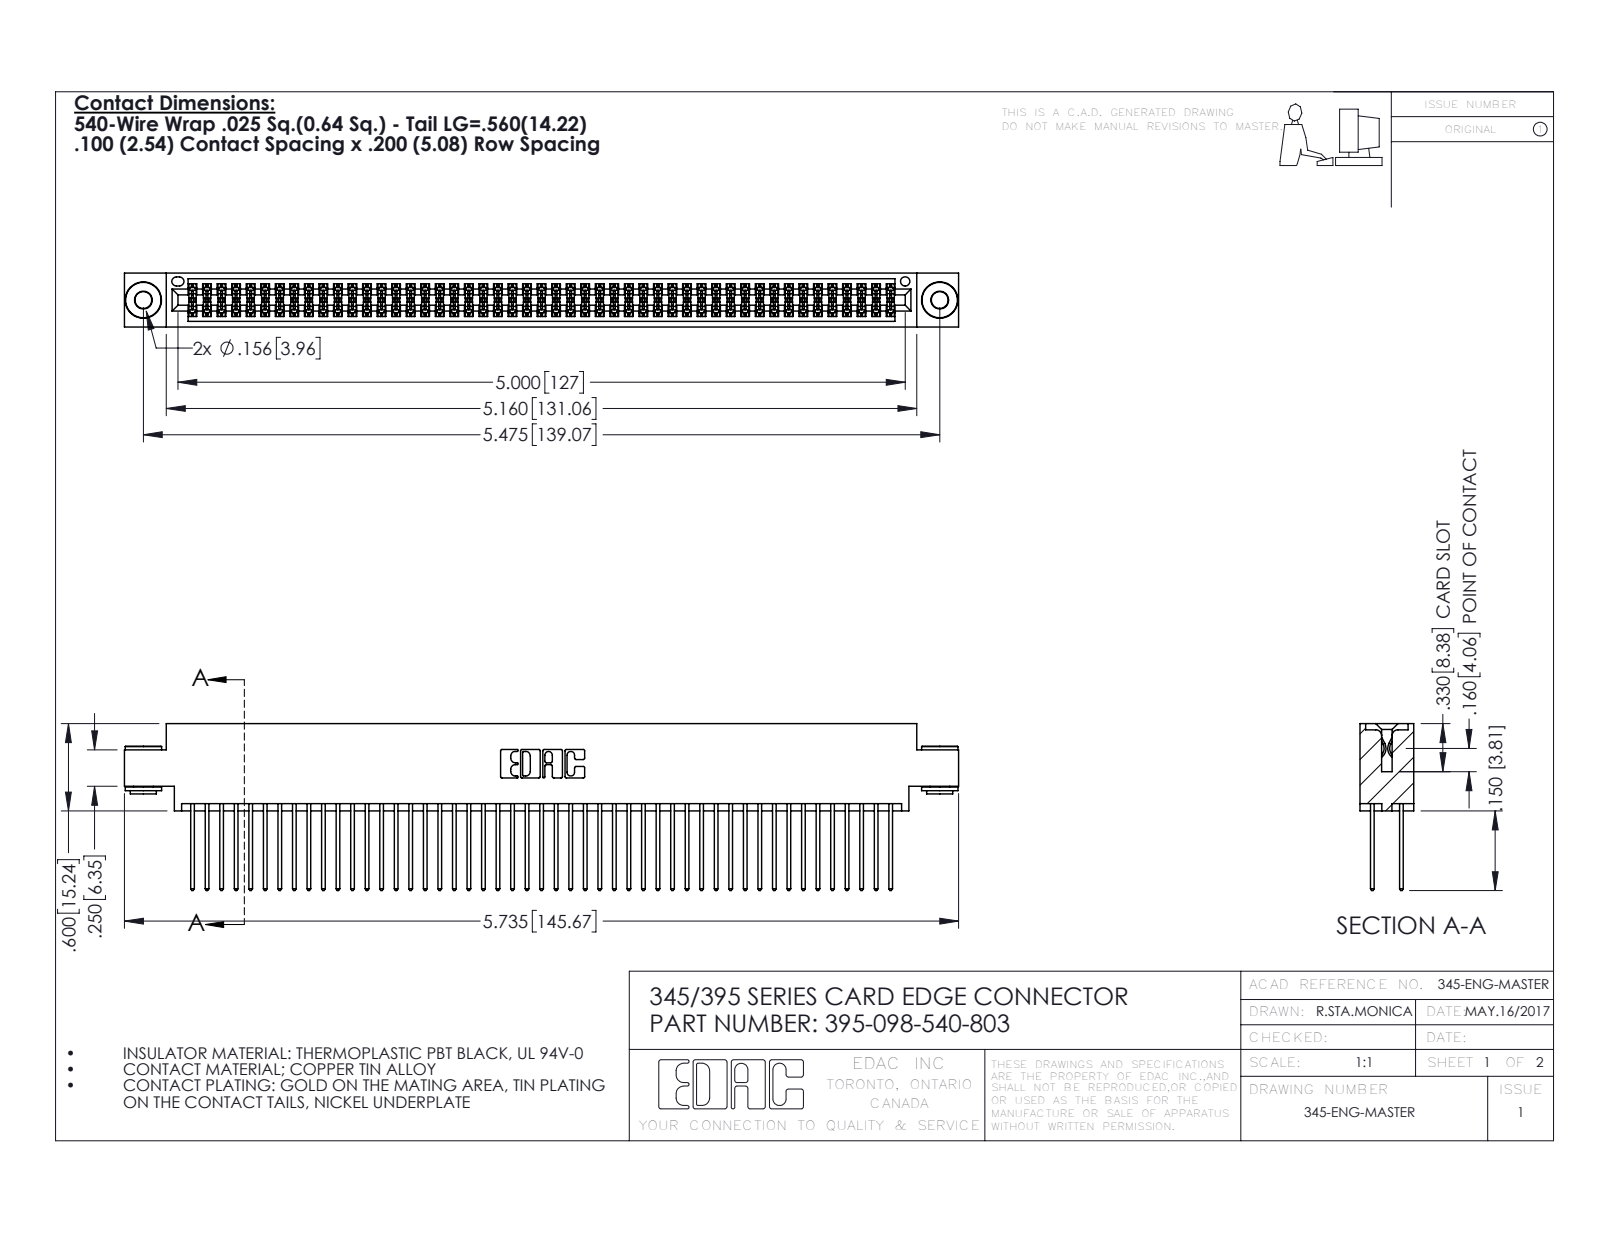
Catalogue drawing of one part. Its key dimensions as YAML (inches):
part_name: "345 Part_0.170 Offset - 0.156 Dia-TH; 345-250-002_345-250-002-102; 395-098-540-803; 345-292-001_345-293-140"
step_written_by: "SolidWorks 2016 (CONFIG_CONTROL_DESIGN)"
units: inches
bodies: {solids: 101, faces: 5068, planar: 3328, cylindrical: 1732, other: 8}
overall_size: [5.735, 1.147, 0.37]
volume: 0.884
surface_area: 36.63
round_holes:
  - {diameter: 0.116, count: 2}
  - {diameter: 0.156, count: 2}
  - {diameter: 0.064, count: 1}
round_bosses_or_shafts:
  - {diameter: 0.25, count: 2}
  - {diameter: 0.18, count: 2}
  - {diameter: 0.136, count: 2}
partial_cylinders:
  - {radius: 0.006, count: 147}
  - {radius: 0.01, count: 98}
  - {radius: 0.01, count: 22}
  - {radius: 0.007, count: 6}
  - {radius: 0.031, count: 6}
  - {radius: 0.026, count: 3}
  - {radius: 0.014, count: 2}
  - {radius: 0.019, count: 2}
face_to_face_distances: [0.072, 0.298, 0.2, 0.098, 0.272, 0.025, 0.37, 0.225, 0.175, 0.149]
hole_center_spacings: [0.27, 5.239, 5.475]
